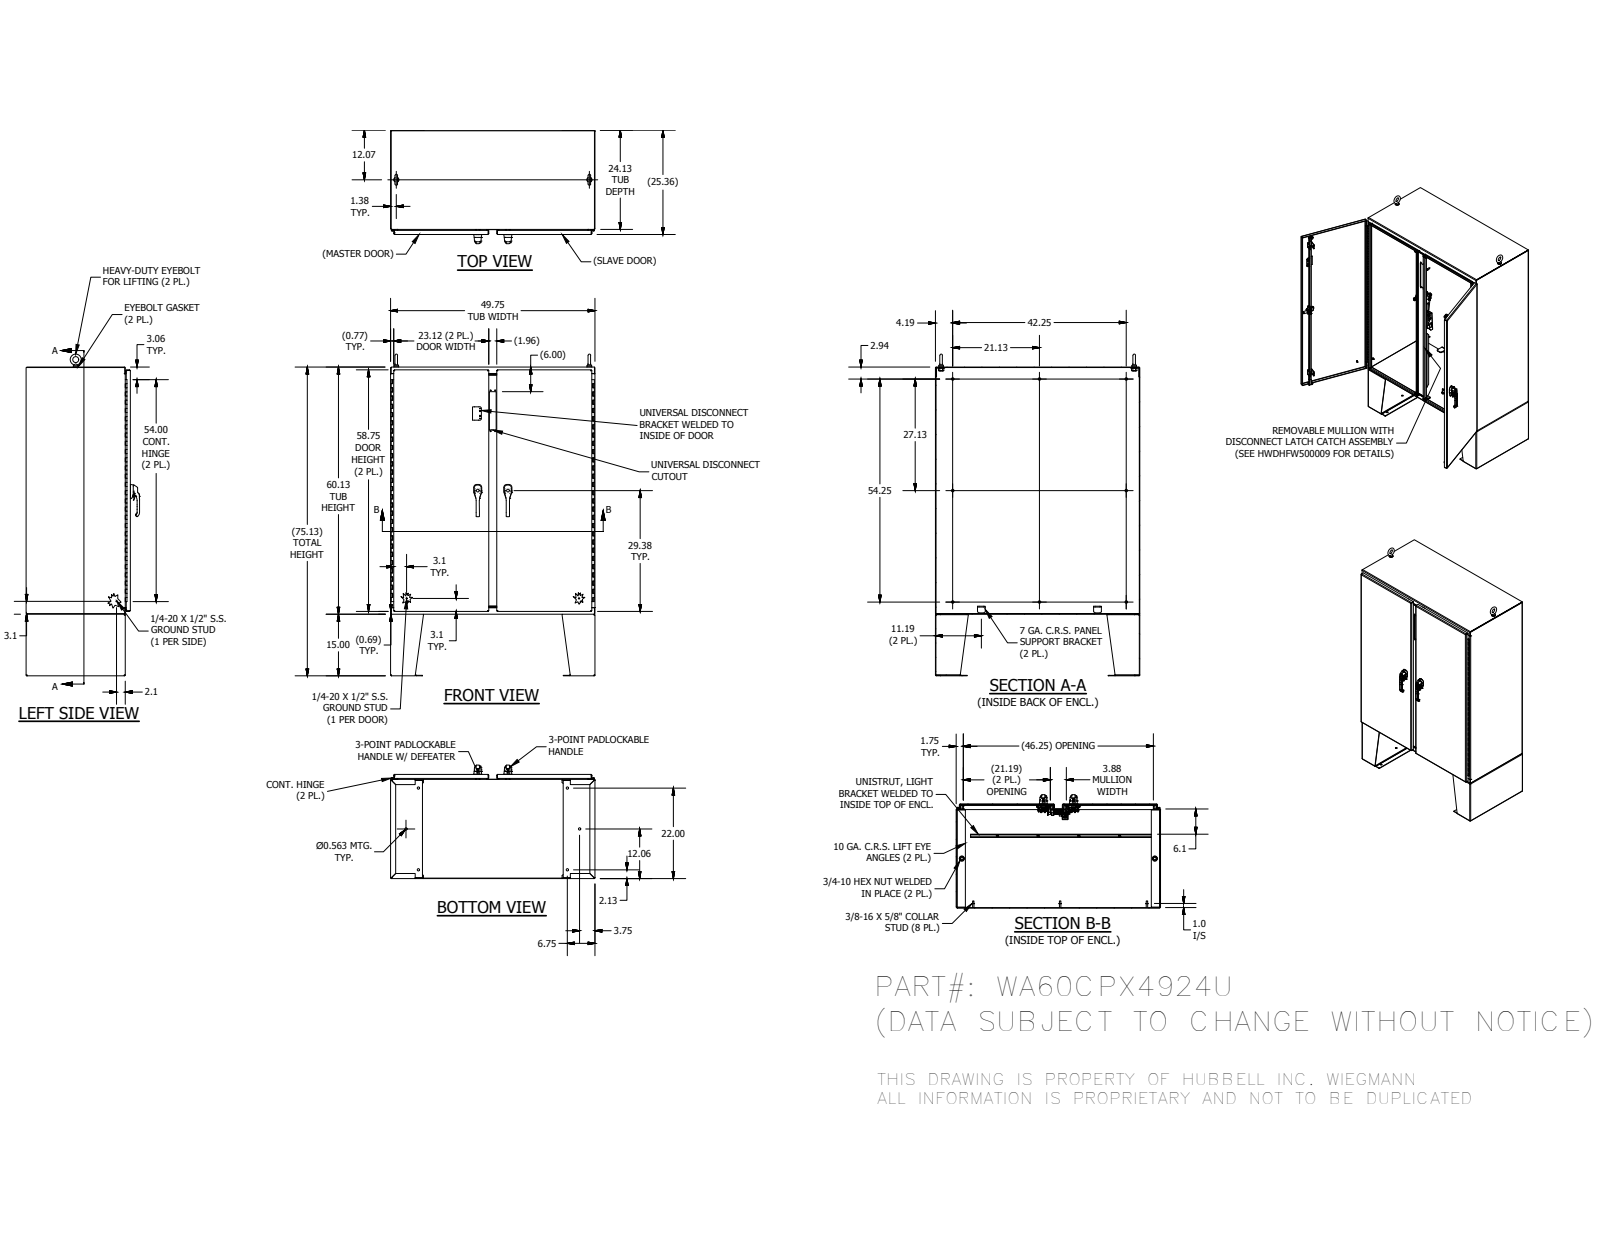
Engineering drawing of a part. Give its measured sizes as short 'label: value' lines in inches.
name: WA60CPX4924UBLR; WACPX4924UTOP; WACPX4924UBTM; 30364 (+8 more)
written by: Autodesk Inventor 2016 (AUTOMOTIVE_DESIGN)
unit: in
bodies: 207 solids, 8461 faces (3907 planar, 2837 cylindrical, 1717 other)
size: 78.248 × 49.75 × 27.608
volume: 1 958 in³; area: 30 410 in²
holes: 21× ⌀0.25, 18× ⌀0.375, 18× ⌀0.563, 8× ⌀0.2, 8× ⌀0.203, 8× ⌀0.276, 8× ⌀0.313, 6× ⌀0.156, 6× ⌀0.19, 6× ⌀0.196, 6× ⌀0.201, 6× ⌀0.213
bosses: 19× ⌀0.25, 16× ⌀0.33, 14× ⌀0.625, 9× ⌀0.563, 9× ⌀0.375, 9× ⌀0.337, 8× ⌀1, 8× ⌀0.438
rounds: 344× R0.02, 202× R0.012, 144× R0.02, 42× R0.019, 40× R0.05, 40× R0.125, 37× R0.094, 27× R0.079
face distances: 0.134, 0.134, 25.217, 49.616, 25.083, 25.35, 59.991, 49.482, 49.75, 0.125
hole spacings: 1.102, 7.334, 2.759, 7.387, 0.886, 1.142, 1.195, 1.271
